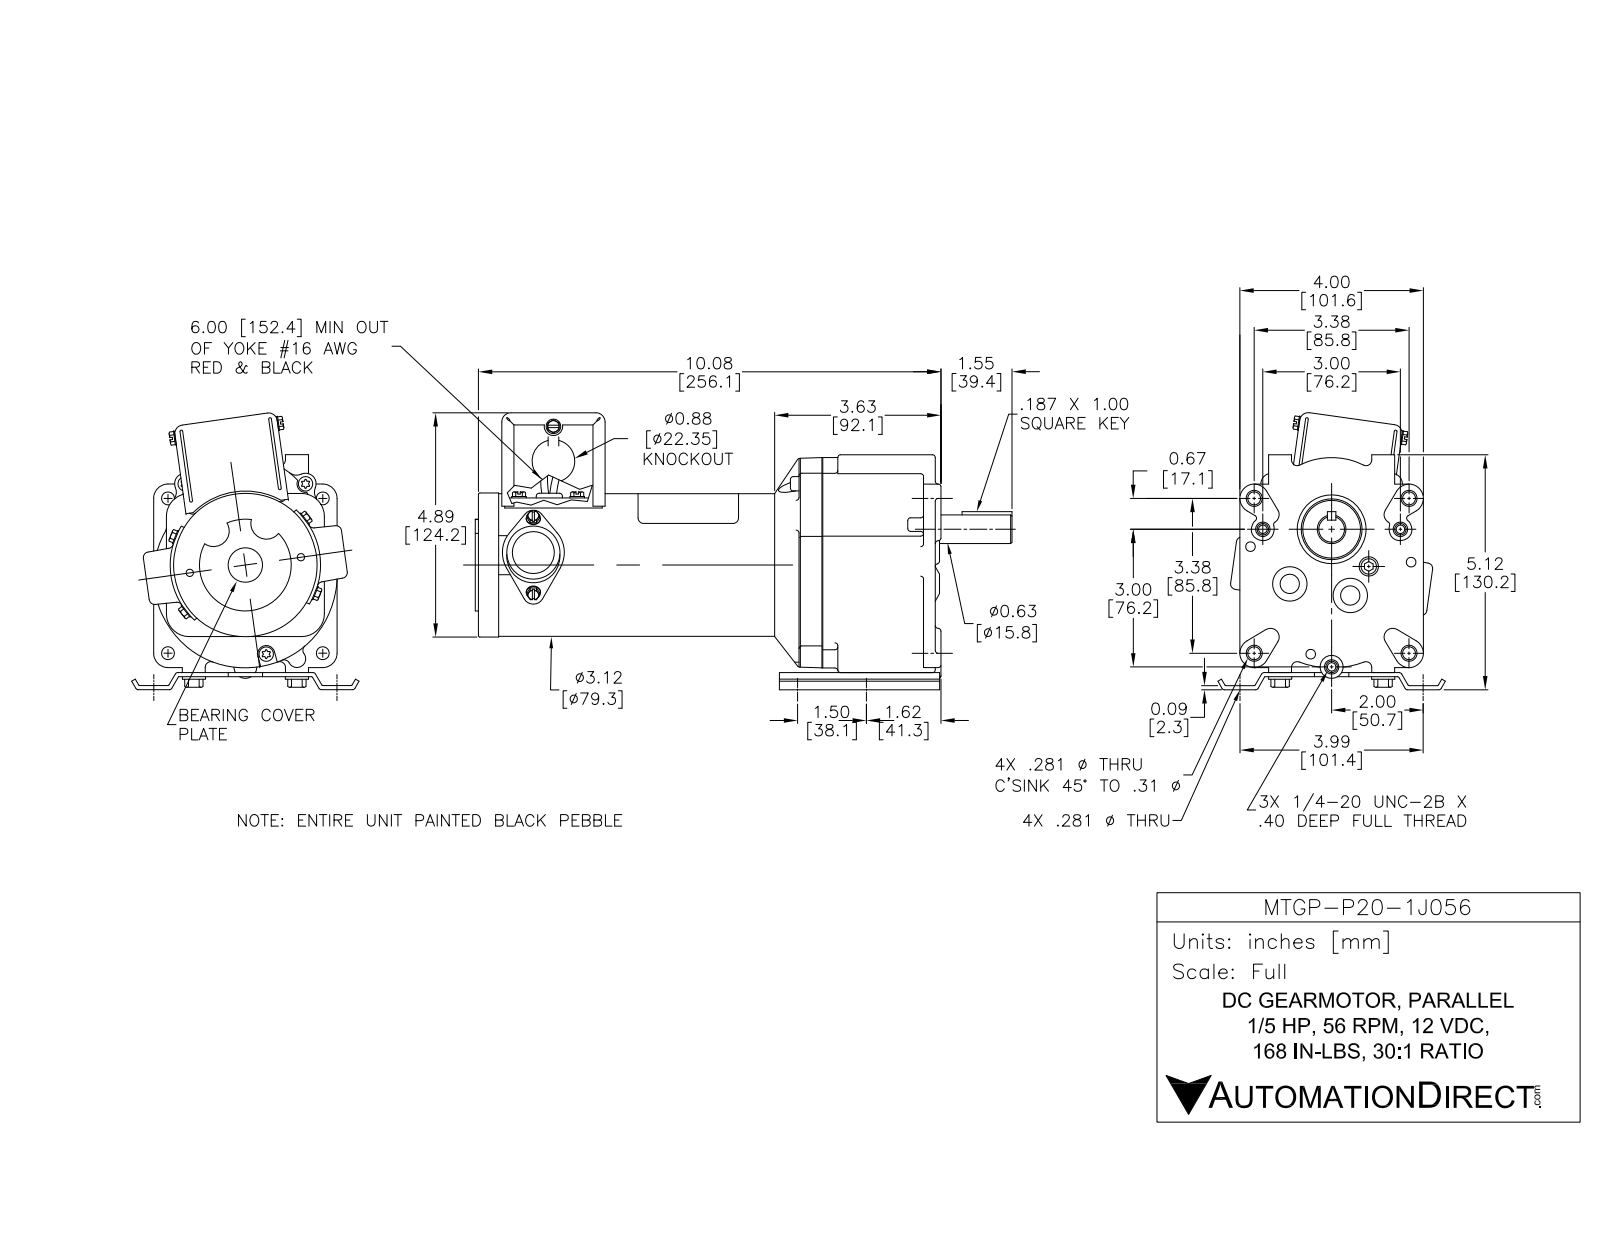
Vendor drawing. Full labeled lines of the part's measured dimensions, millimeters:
Part name (STEP PRODUCT): MTGP-P20-1J056
STEP written by: SolidWorks 2014 (AUTOMOTIVE_DESIGN)
Units: millimetres
Bodies: 53 solids, 984 faces (567 planar, 365 cylindrical, 52 other)
Overall size (bounding box): 297.1 × 157.7 × 125.5
Volume: 1 067 000 mm³ · Surface area: 303 600 mm²
Round holes (diameter × count): ⌀7.6 ×11, ⌀12.7 ×5, ⌀6.4 ×4, ⌀8.8 ×4, ⌀5.3 ×3, ⌀3.2 ×2, ⌀5 ×2, ⌀5.3 ×2, ⌀8.8 ×2, ⌀9.5 ×1, ⌀11.7 ×1, ⌀15.9 ×1
Round bosses / shafts (diameter × count): ⌀8 ×5, ⌀7.6 ×4, ⌀5.3 ×3, ⌀11.7 ×2, ⌀2.5 ×2, ⌀80.2 ×1, ⌀33.7 ×1, ⌀15.9 ×1
Partial cylindrical surfaces — rounded edges, fillets, slot ends (radius × count): R0.5 ×28, R2.5 ×23, R0.6 ×8, R6.4 ×7, R4 ×4, R4.8 ×4, R4.9 ×4, R5.9 ×4
Main face-to-face distances: 34.9, 88.8, 53.8, 2.3, 0.8, 6.4, 1.6, 1.3, 36.2, 90
Hole centre spacings: 41.1, 31.2, 38.1, 38.2, 40.7, 75.5, 85.7, 175.5
